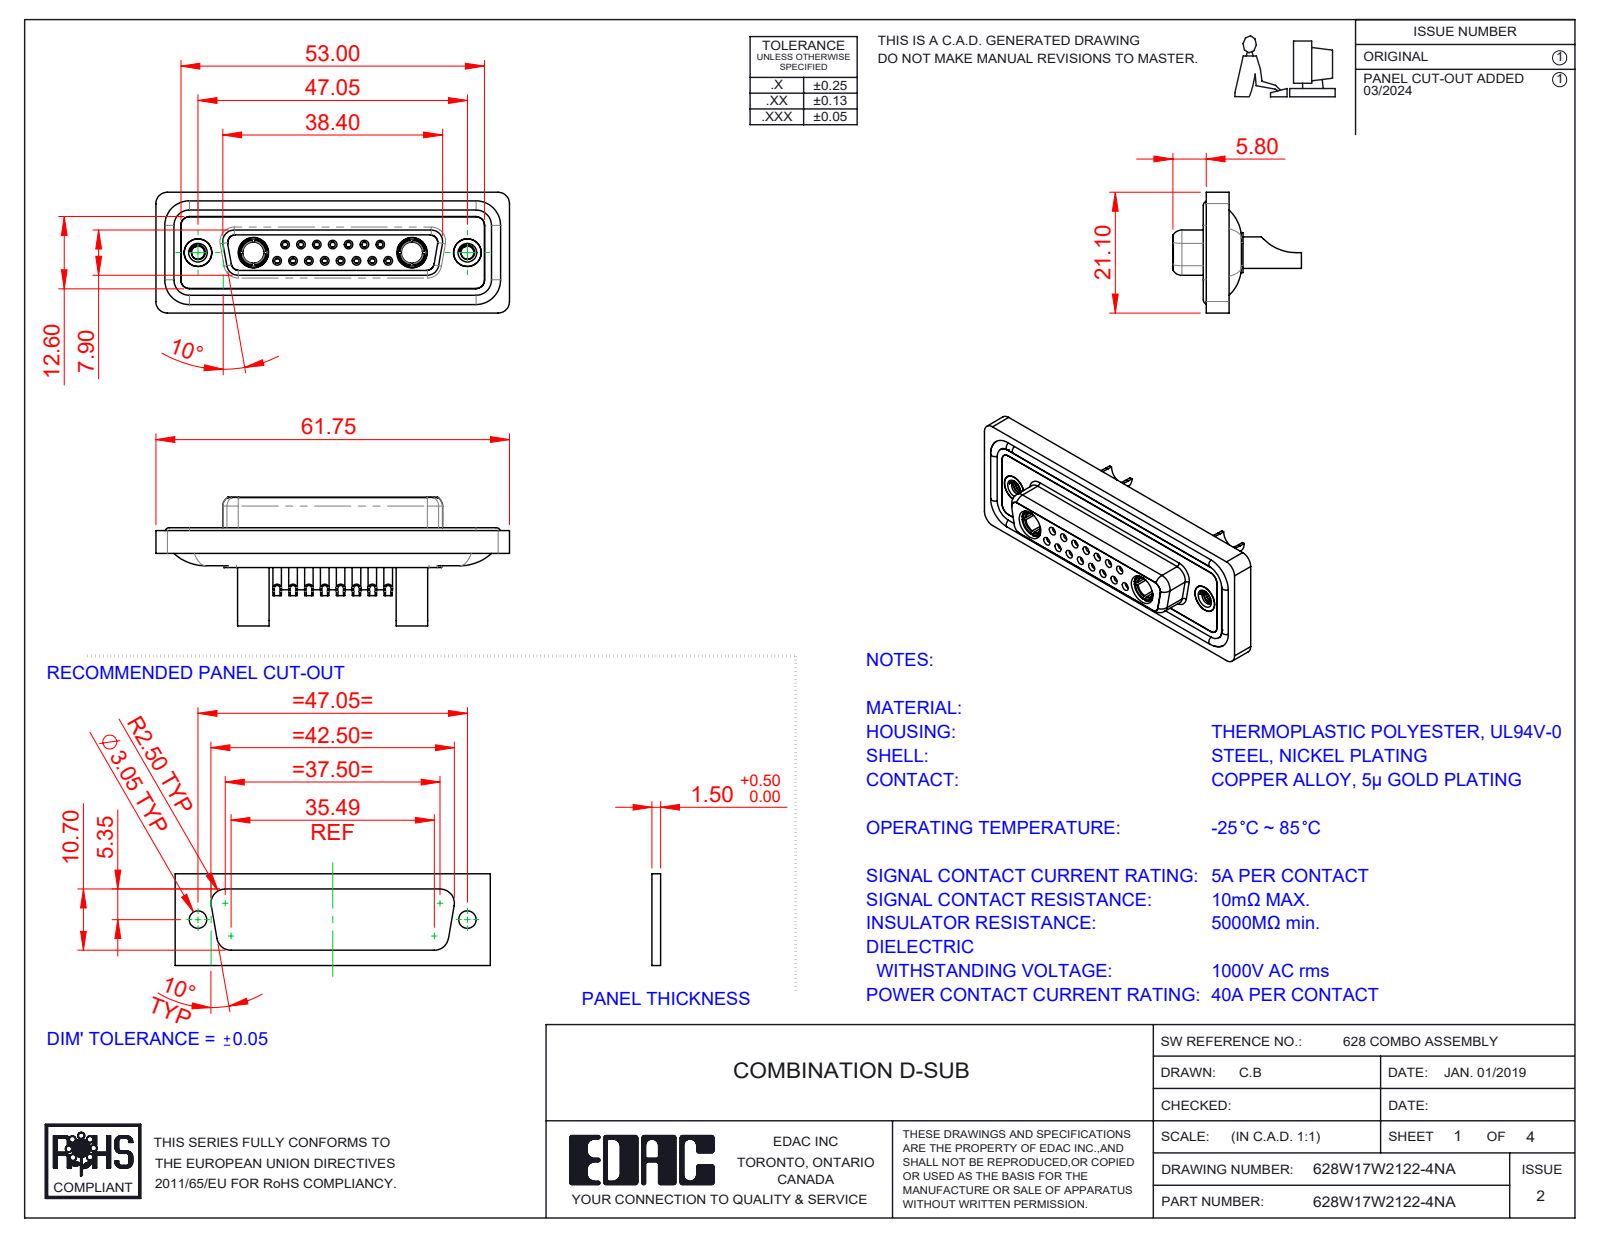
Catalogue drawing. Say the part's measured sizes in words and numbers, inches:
The part is named "628Combo Shell Rear_25 Contacts; 628Combo Contact Row 1_22; 628Combo Contact Row 2_22; 628W17W2122-4NA (+5 more)". Its 3-D file was written by "SolidWorks 2023 (CONFIG_CONTROL_DESIGN)". It is 26 solids with 1363 faces: 422 planar, 553 cylindrical and 388 other. Overall it measures 2.431 by 0.884 by 0.831 inches. Its volume is 0.515 cubic inches and its surface area 22.15 square inches. Round holes: 15 of diameter 0.035, 15 of diameter 0.039, 15 of diameter 0.043, 15 of diameter 0.059, 15 of diameter 0.079, 8 of diameter 0.063, 7 of diameter 0.067, 4 of diameter 0.191, 2 of diameter 0.089, 2 of diameter 0.146, 2 of diameter 0.157, 2 of diameter 0.159. Round bosses or shafts: 15 of diameter 0.087, 11 of diameter 0.063, 2 of diameter 0.217, 2 of diameter 0.205, 2 of diameter 0.195, 2 of diameter 0.195, 2 of diameter 0.189, 2 of diameter 0.187. Partial cylindrical surfaces (rounded edges, fillets, slot ends): 22 of radius 0.059, 18 of radius 0.079, 8 of radius 0.053, 8 of radius 0.063, 6 of radius 0.039, 4 of radius 0.01, 4 of radius 0.02, 4 of radius 0.024. The main face-to-face distances are 0.016, 0.293, 0.071, 0.222, 0.26, 0.02, 0.278, 0.063, 0.114, 0.043. The hole center spacings are 0.124, 0.109, 0.327, 0.218, 0.198, 0.198, 0.295, 0.436.
